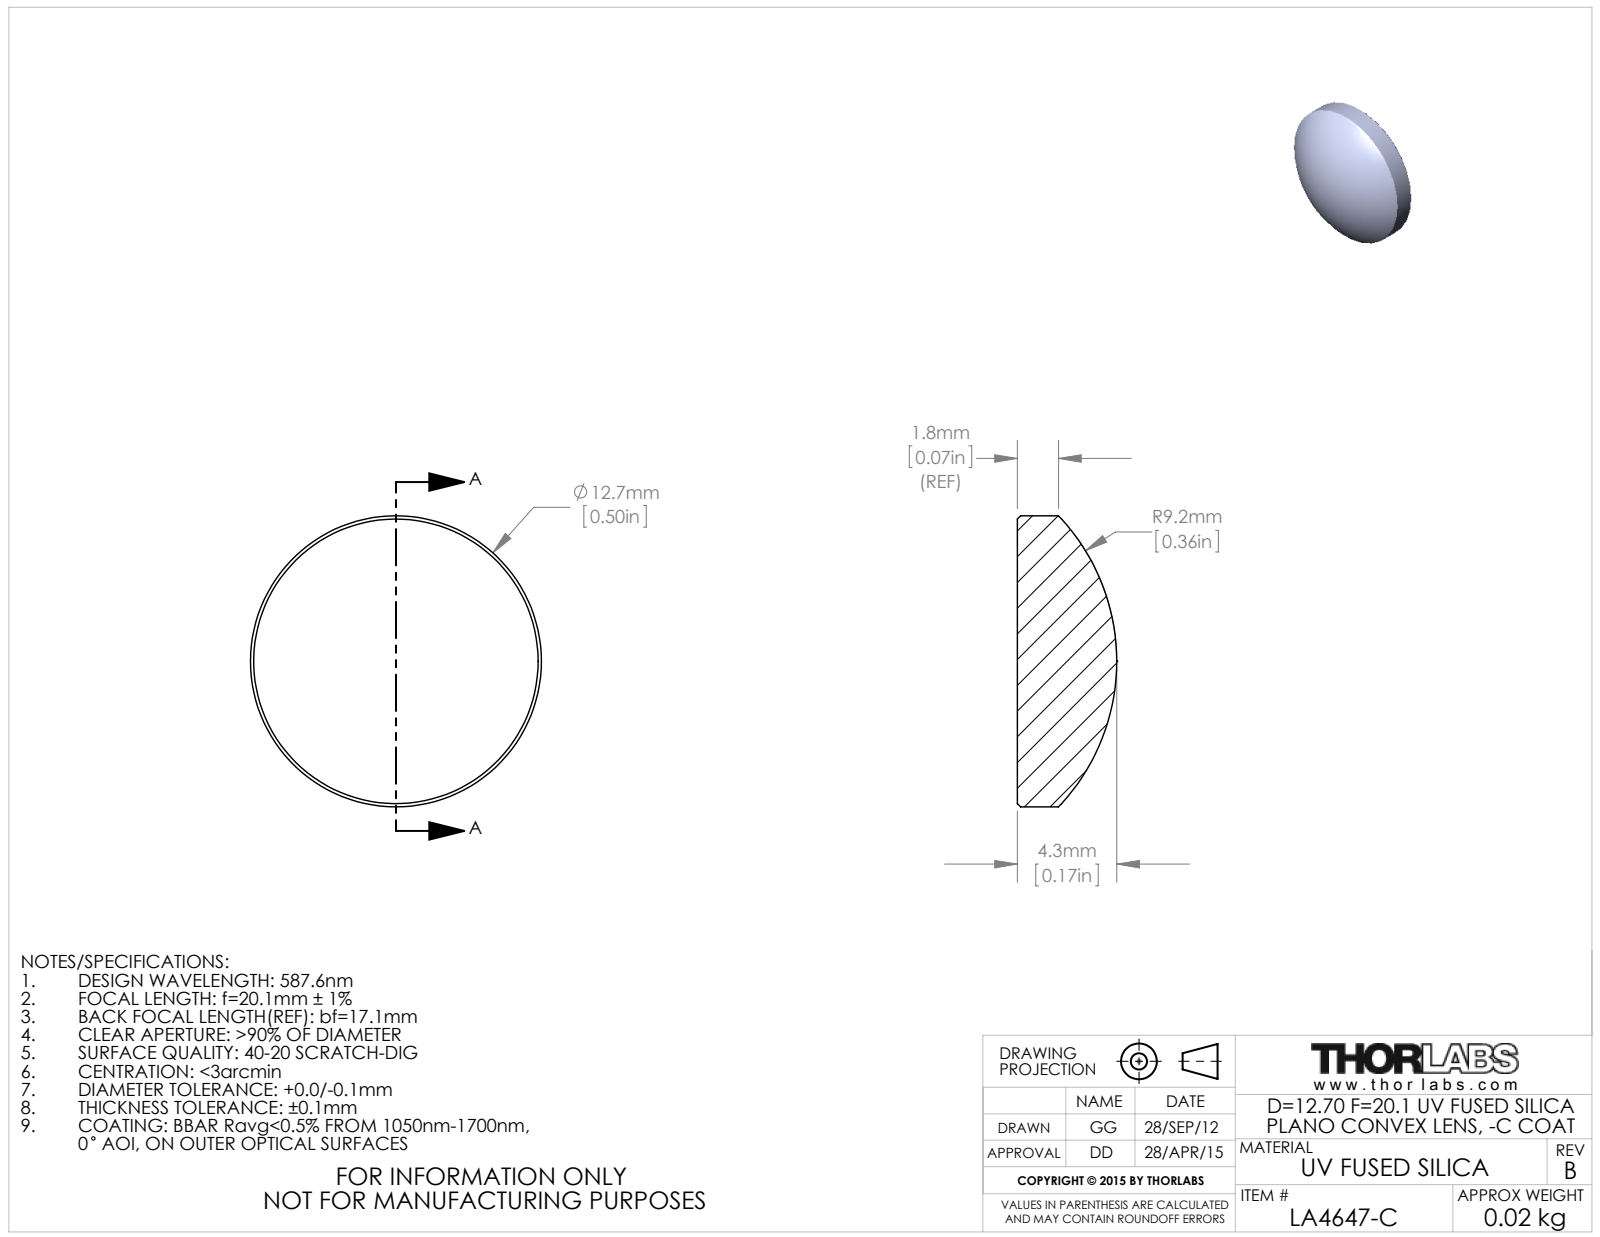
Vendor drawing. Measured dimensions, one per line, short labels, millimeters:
name: 24977-E0W
written by: SolidWorks 2014 (CONFIG_CONTROL_DESIGN)
unit: mm
bodies: 1 solid, 9 faces (1 planar, 2 cylindrical, 6 other)
size: 12.7 × 12.7 × 4.34
volume: 397 mm³; area: 342 mm²
bosses: 1× ⌀12.7
